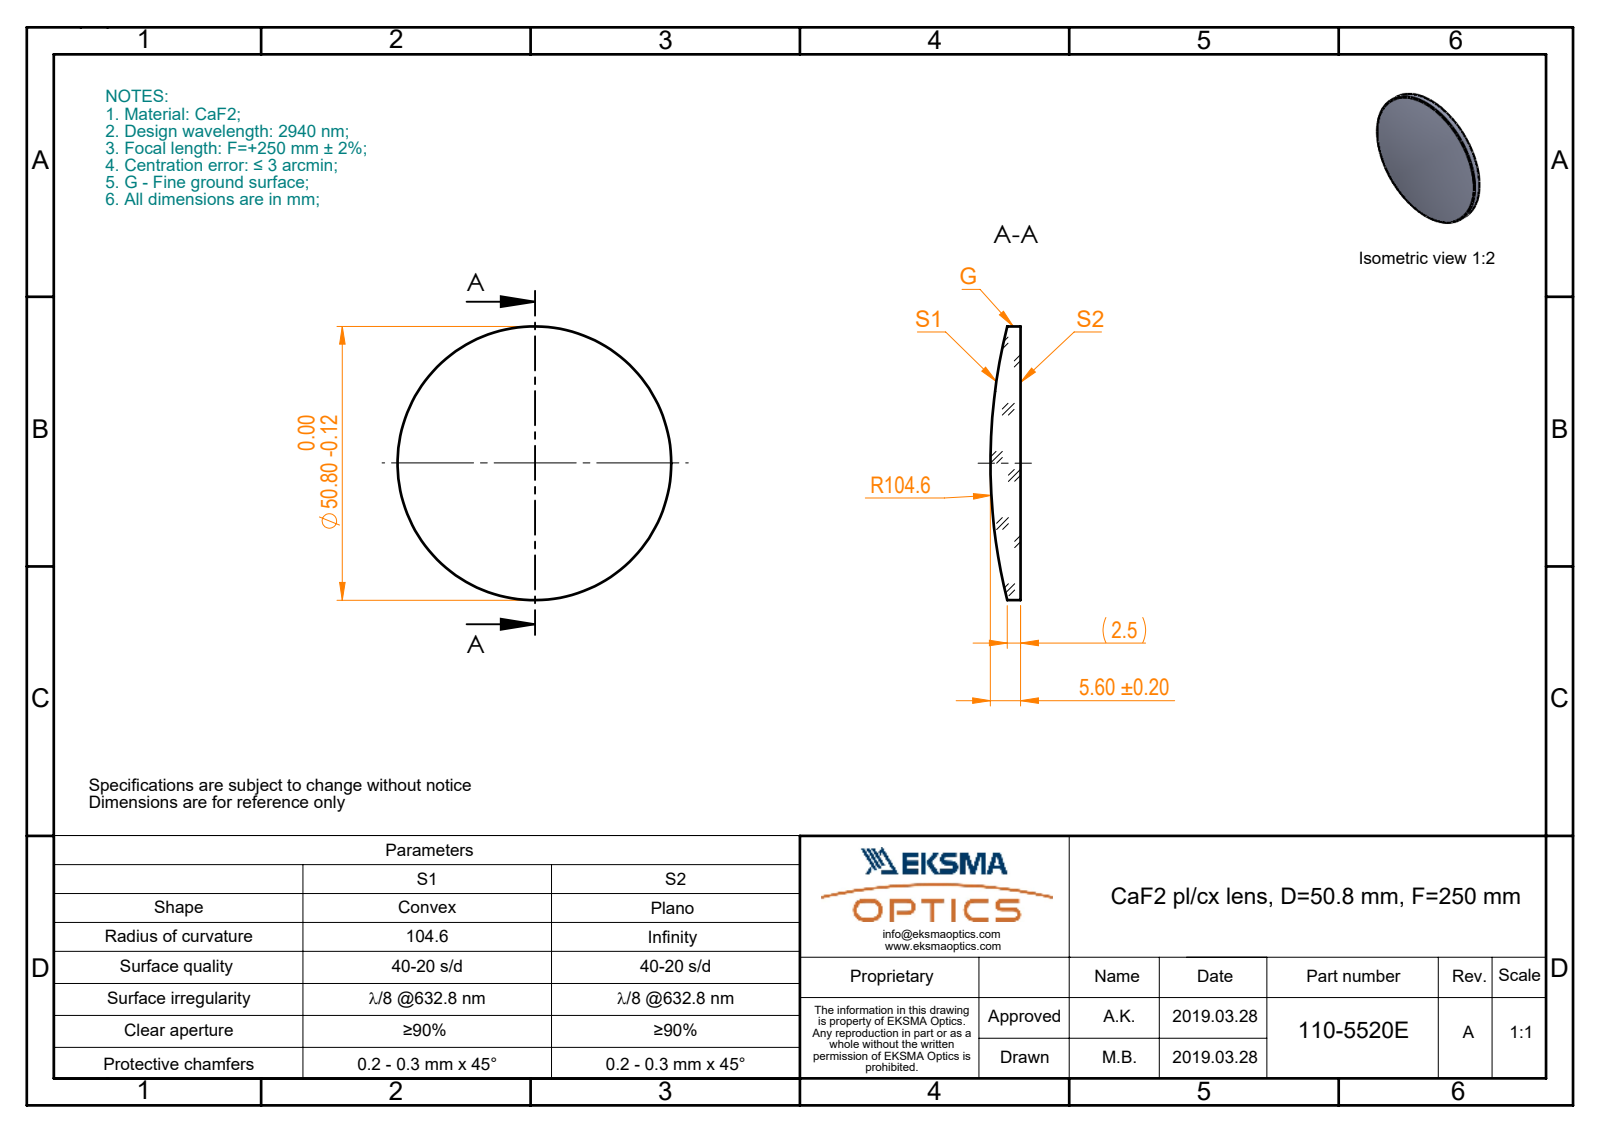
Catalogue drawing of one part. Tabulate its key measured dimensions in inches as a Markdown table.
| quantity | value |
| --- | --- |
| part name | 110-5520E CaF2 pl-cx 50.8 F250 |
| STEP written by | SolidWorks 2017 (CONFIG_CONTROL_DESIGN) |
| units | inches |
| bodies | 1 solid, 5 faces (1 planar, 2 cylindrical, 2 other) |
| overall size | 2 × 2 × 0.22 |
| volume | 0.5 in³ |
| surface area | 6.942 in² |
| round bosses / shafts (diameter × count) | 2 × 1 |
